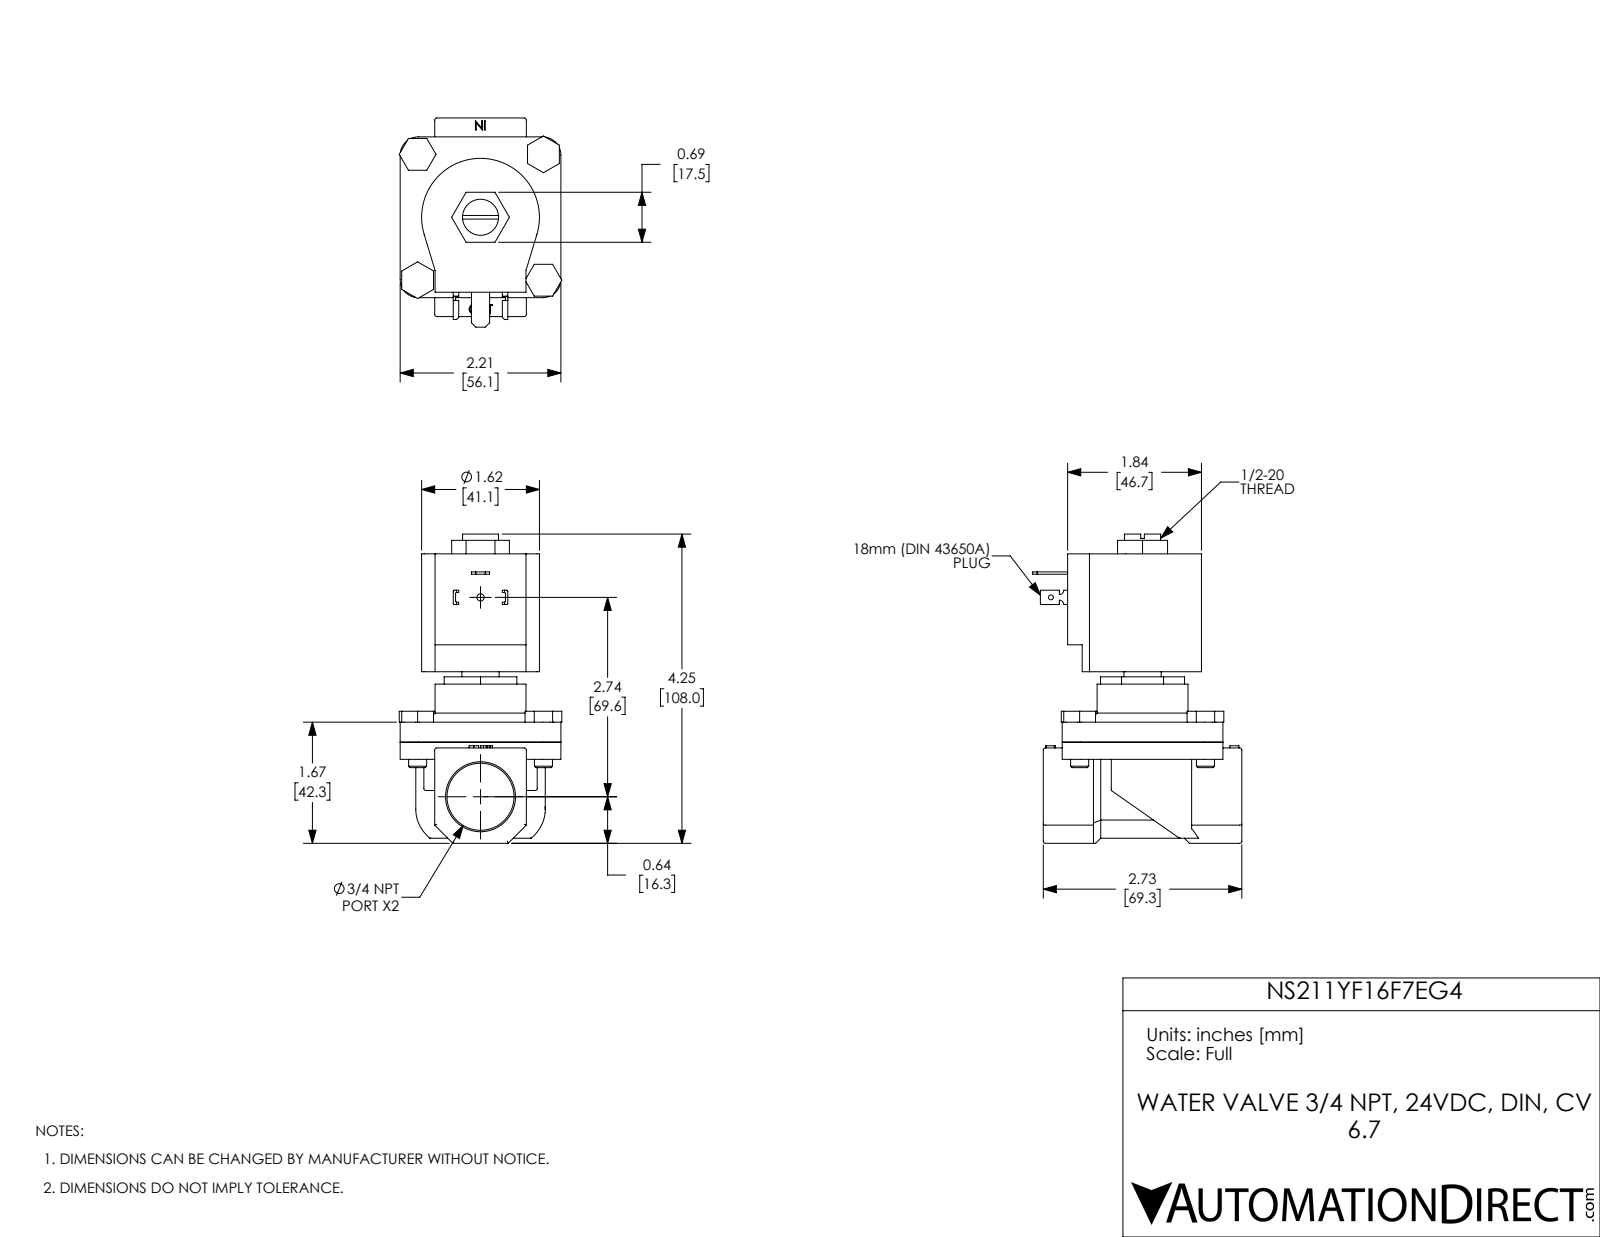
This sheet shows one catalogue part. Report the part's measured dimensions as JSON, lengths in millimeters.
{"part_name": "NS211YF16F7EG5", "step_written_by": "SolidWorks 2017 (AUTOMOTIVE_DESIGN)", "units": "millimeters", "bodies": {"solids": 11, "faces": 332, "planar": 198, "cylindrical": 99, "other": 35}, "overall_size": [108, 73, 56.8], "volume_mm3": 171700, "surface_area_mm2": 43050, "round_holes": [[6.4, 4], [1.7, 1], [2.5, 1], [12.6, 1], [13, 1], [23.4, 1], [29.3, 1]], "round_bosses_or_shafts": [[6.3, 4], [31.8, 1]], "partial_cylinders_radius": [[0.8, 15], [0.4, 8], [6.4, 4], [1.5, 2], [20.6, 1], [22.6, 1]], "face_to_face_distances": [7, 65.7, 58.8, 12.1, 44.1, 56.1, 6, 13, 71.7, 6.6], "hole_center_spacings": [31.1, 43.9, 62.1, 69.6]}
